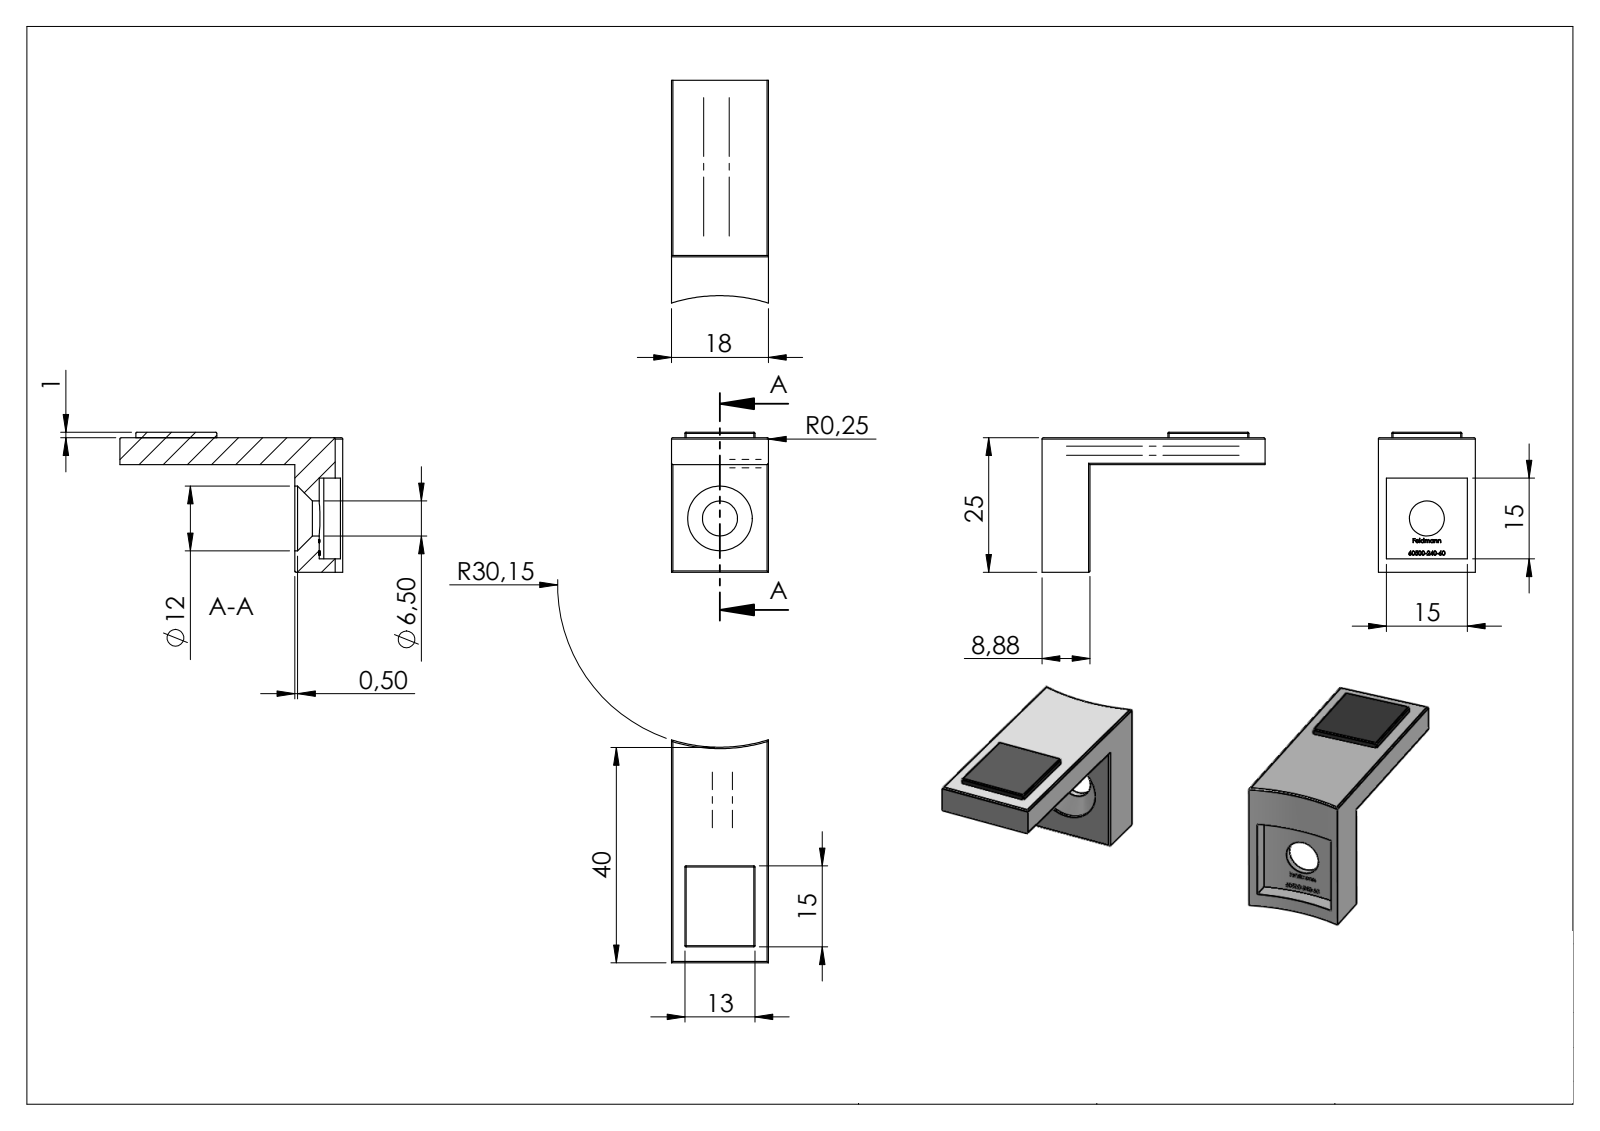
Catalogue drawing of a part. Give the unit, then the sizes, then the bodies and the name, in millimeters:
Units: millimetres
Overall size (bounding box): 41.38 × 26 × 18
Round holes (diameter × count): ⌀6.5 ×1, ⌀12 ×1
Partial cylindrical surfaces — rounded edges, fillets, slot ends (radius × count): R0.2 ×8, R0.25 ×8, R30.15 ×1, R33.15 ×1, R33.25 ×1
Main face-to-face distances: 5, 18, 1, 6, 20, 25, 26, 2.5, 15, 1.5
Volume: 5 724 mm³ · Surface area: 3 749 mm²
Bodies: 2 solids, 306 faces (123 planar, 55 cylindrical, 128 other)
Part name (STEP PRODUCT): 60500-240-60
STEP written by: SolidWorks 2015 (CONFIG_CONTROL_DESIGN)
